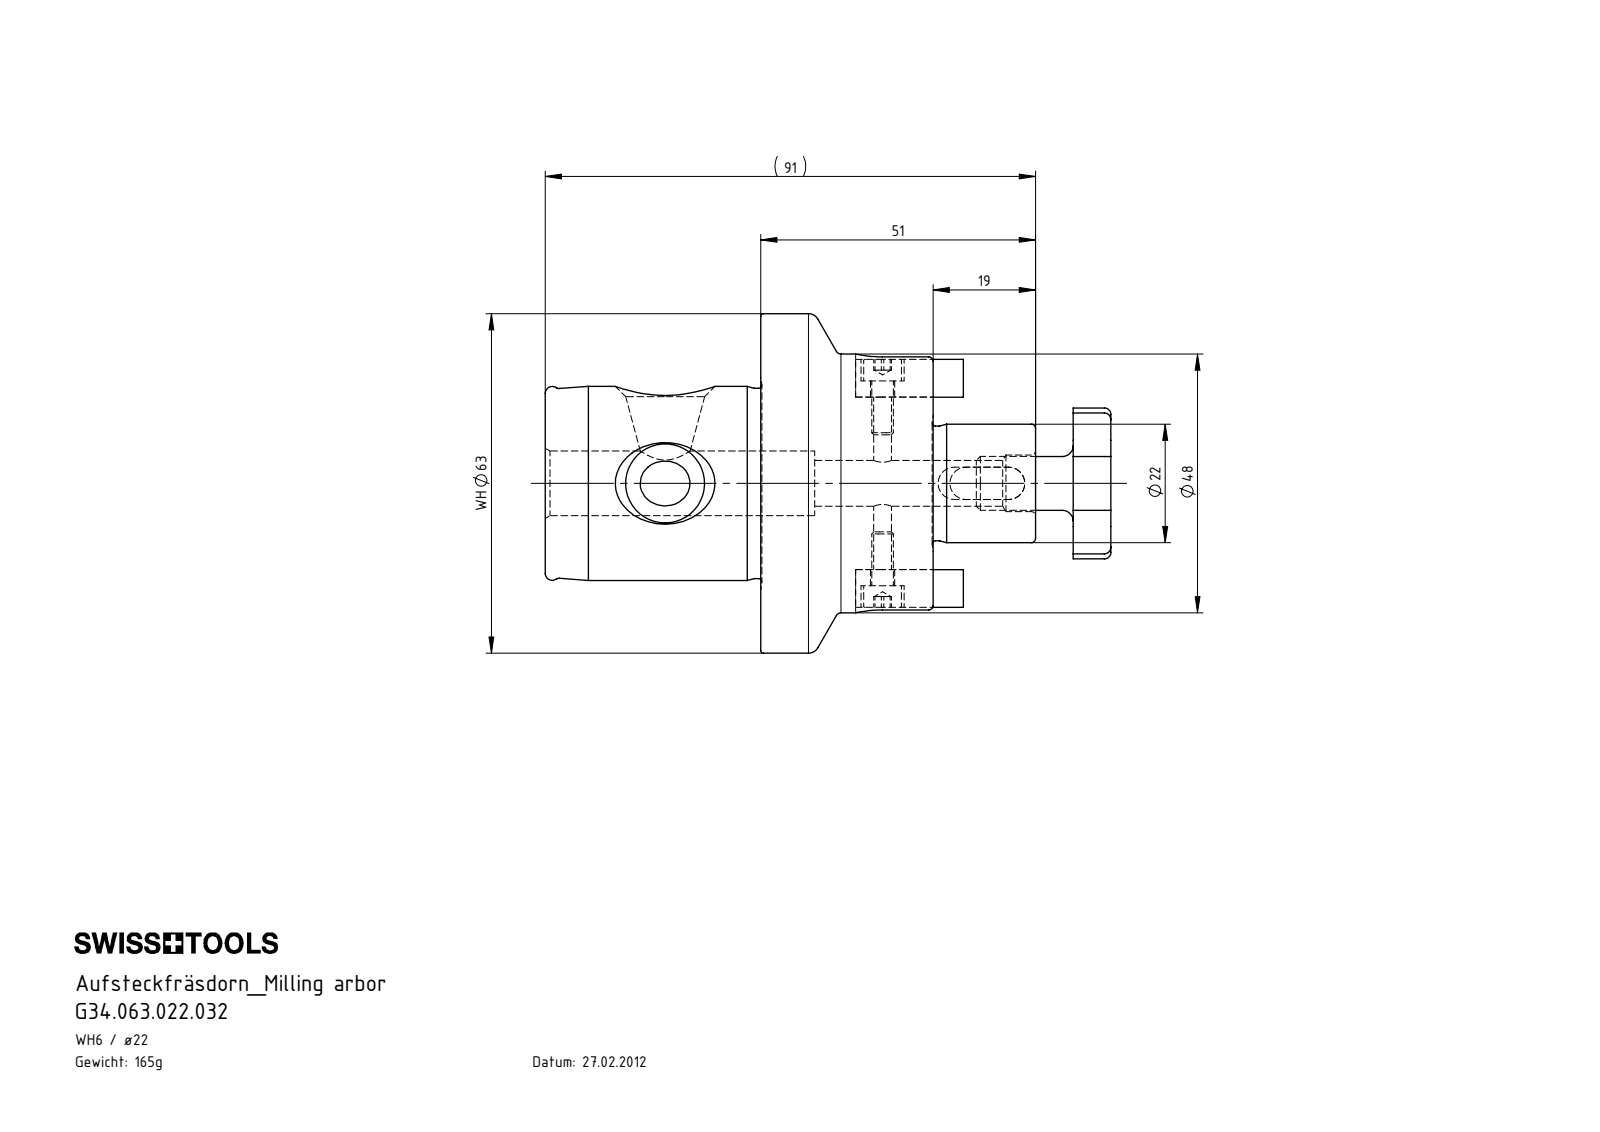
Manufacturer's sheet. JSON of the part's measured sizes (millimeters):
{"part_name": "WH6.D22.001.032; D22-ER3.001.014_A; D22-ER1.001.018_A; D22-ER2.002.010_A (+2 more)", "step_written_by": "SolidWorks 2022 (AUTOMOTIVE_DESIGN)", "units": "millimeters", "bodies": {"solids": 7, "faces": 210, "planar": 71, "cylindrical": 60, "other": 79}, "overall_size": [105, 63, 63], "volume_mm3": 115150, "surface_area_mm2": 25588, "round_holes": [[3.3, 1], [4.5, 1], [8, 1], [8.5, 1], [10.5, 1], [12, 1]], "round_bosses_or_shafts": [[63, 1], [48, 1], [36, 1], [35.3, 1], [22, 1], [21.3, 1], [10, 1], [7, 1]], "partial_cylinders_radius": [[3, 7], [5, 1], [14, 1]], "face_to_face_distances": [32, 7, 40, 72, 10, 26, 105, 65, 33, 19]}
